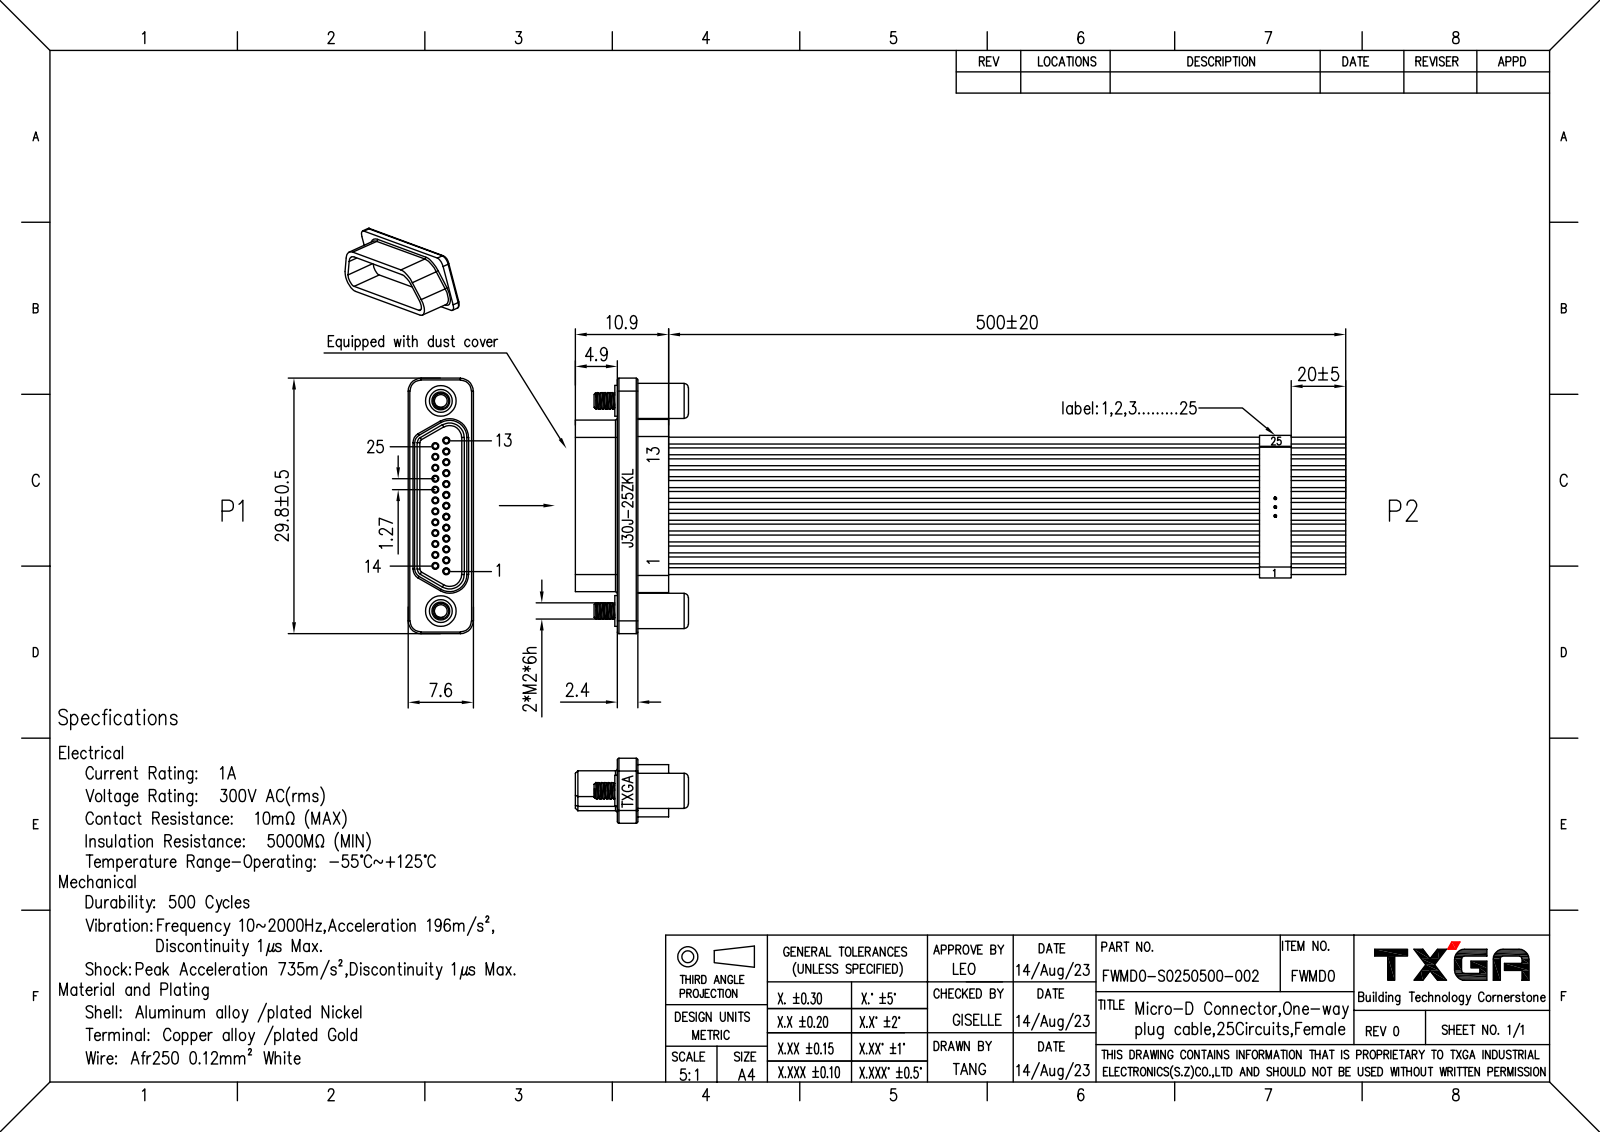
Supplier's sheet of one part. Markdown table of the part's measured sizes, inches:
| quantity | value |
| --- | --- |
| part name | ZHUTI-25-1; PINZHEN3; LUOSISHELL; LUOS (+3 more) |
| STEP written by | PRO/ENGINEER BY PARAMETRIC TECHNOLOGY CORPORATION, 2010280 (CONFIG_CONTROL_DESIGN) |
| units | inches |
| bodies | 56 solids, 865 faces (385 planar, 350 cylindrical, 130 other) |
| overall size | 3.539 × 1.173 × 0.299 |
| volume | 0.137 in³ |
| surface area | 12.87 in² |
| round holes (diameter × count) | 0.024 × 25, 0.031 × 5, 0.083 × 2, 0.11 × 2, 0.126 × 2, 0.138 × 2 |
| round bosses / shafts (diameter × count) | 0.031 × 27, 0.161 × 2, 0.142 × 2, 0.128 × 2, 0.075 × 2 |
| partial cylindrical surfaces (radius × count) | 0.008 × 28, 0.055 × 8, 0.059 × 4, 0.079 × 4, 0.016 × 2, 0.039 × 2, 0.063 × 2, 0.087 × 2 |
| main face-to-face distances | 0.024, 0.24, 0.014, 0.23, 0.217, 0.037, 0.254, 0.016, 0.03, 0.053 |
| hole center spacings | 0.056, 0.1, 0.05, 0.091, 0.15, 0.2, 0.135, 0.182 |
